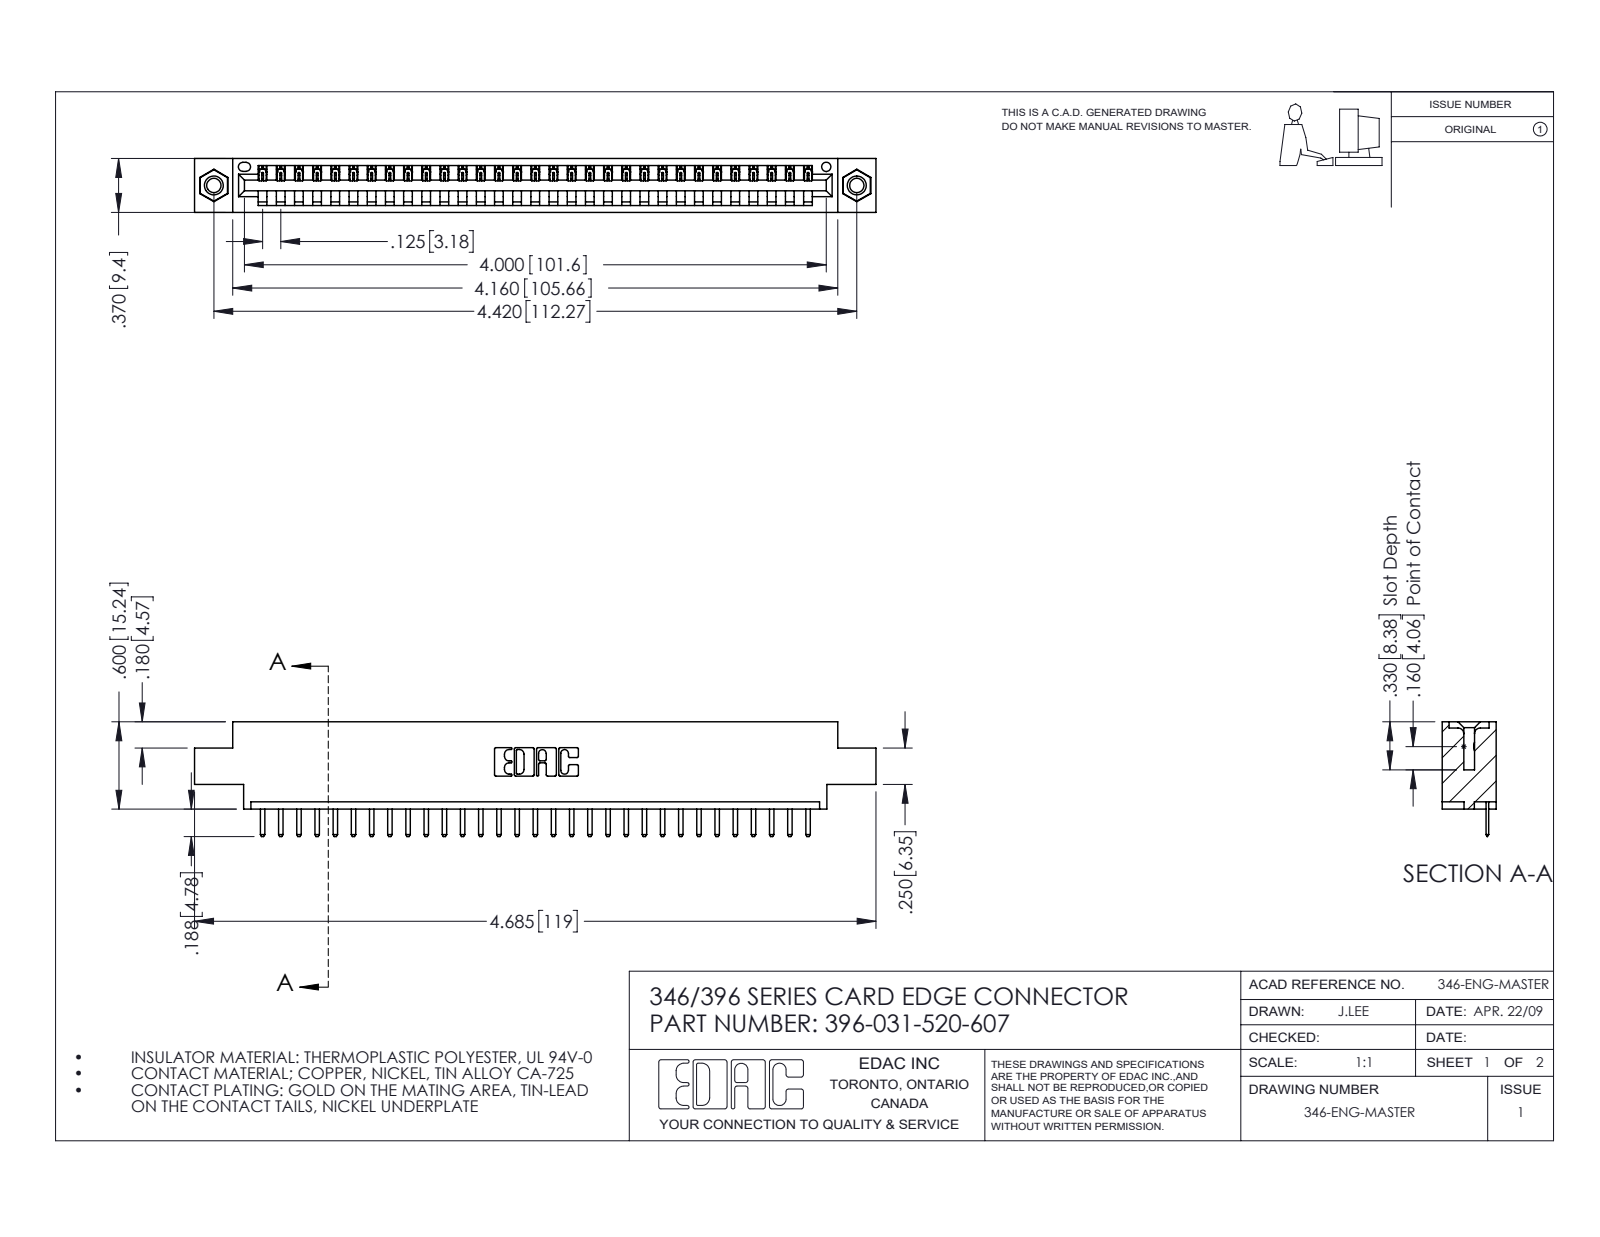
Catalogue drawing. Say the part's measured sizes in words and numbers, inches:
The part is named "396-031-520-607; 345-250-001_345-250-005-103; 346 Part_0.170 Offset - 0.156 Dia-TI; 345-292-001_345-293-120". Its 3-D file was written by "SolidWorks 2016 (CONFIG_CONTROL_DESIGN)". It is 34 solids with 2108 faces: 1414 planar, 678 cylindrical and 16 other. Overall it measures 4.685 by 0.788 by 0.37 inches. Its volume is 0.675 cubic inches and its surface area 21.08 square inches. Round holes: 2 of diameter 0.098, 2 of diameter 0.125, 2 of diameter 0.156, 1 of diameter 0.064. Round bosses or shafts: 2 of diameter 0.155. Partial cylindrical surfaces (rounded edges, fillets, slot ends): 64 of radius 0.01, 62 of radius 0.006, 22 of radius 0.01, 6 of radius 0.007, 6 of radius 0.031, 3 of radius 0.026, 2 of radius 0.031, 2 of radius 0.04. The main face-to-face distances are 0.048, 0.322, 0.37, 0.25, 0.222, 0.148, 0.1, 0.174, 0.072, 0.298. The hole center spacings are 0.246, 4.212, 4.42.
